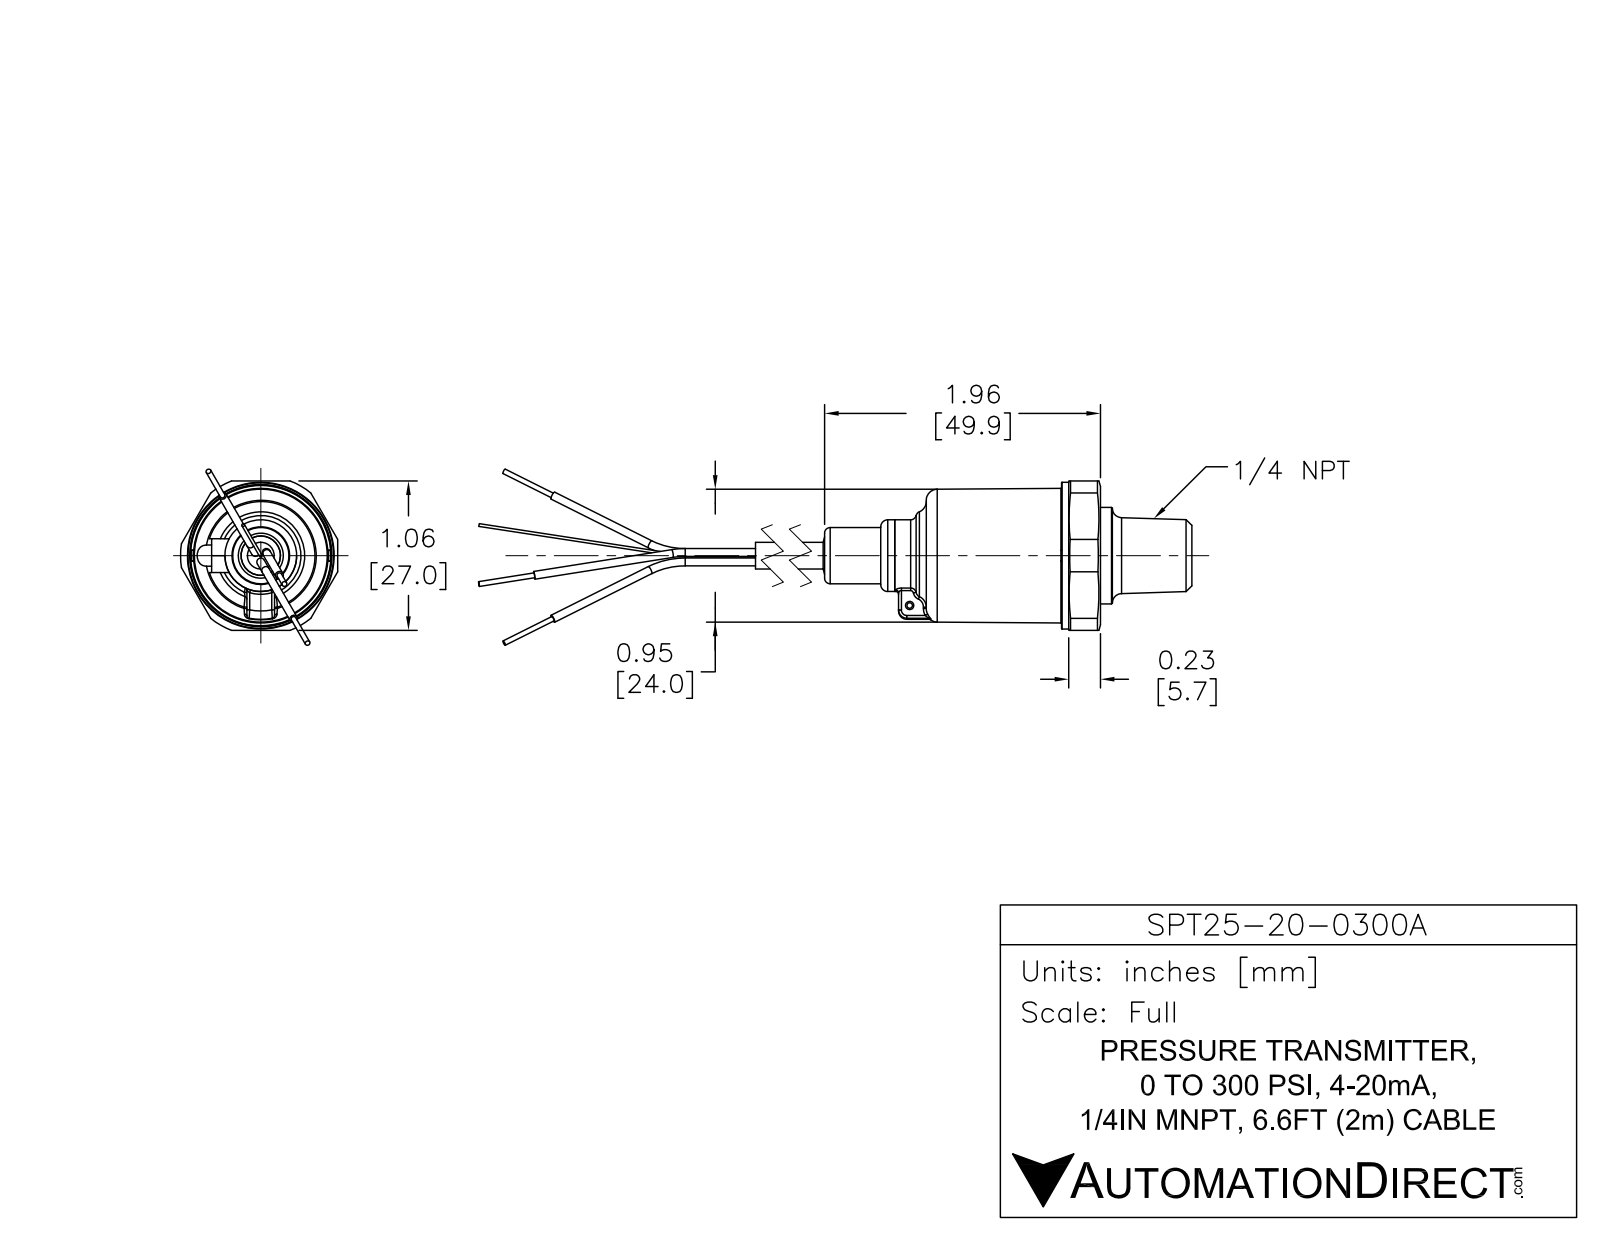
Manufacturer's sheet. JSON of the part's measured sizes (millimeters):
{"part_name": "SPT25-20-0300A", "step_written_by": "SolidWorks 2017 (AUTOMOTIVE_DESIGN)", "units": "millimeters", "bodies": {"solids": 7, "faces": 116, "planar": 32, "cylindrical": 49, "other": 35}, "overall_size": [153.3, 29, 27.09], "volume_mm3": 20801, "surface_area_mm2": 7170, "round_holes": [[1, 1], [3.3, 1]], "round_bosses_or_shafts": [[1.4, 6], [0.75, 5], [26.75, 1], [24, 1], [17.5, 1], [14, 1], [13, 1], [10, 1]], "partial_cylinders_radius": [[2, 1], [14.5, 1]], "face_to_face_distances": [6.75, 24, 17.25, 42.75, 49.5, 66.75, 44, 1.25, 5.5, 22.75]}
